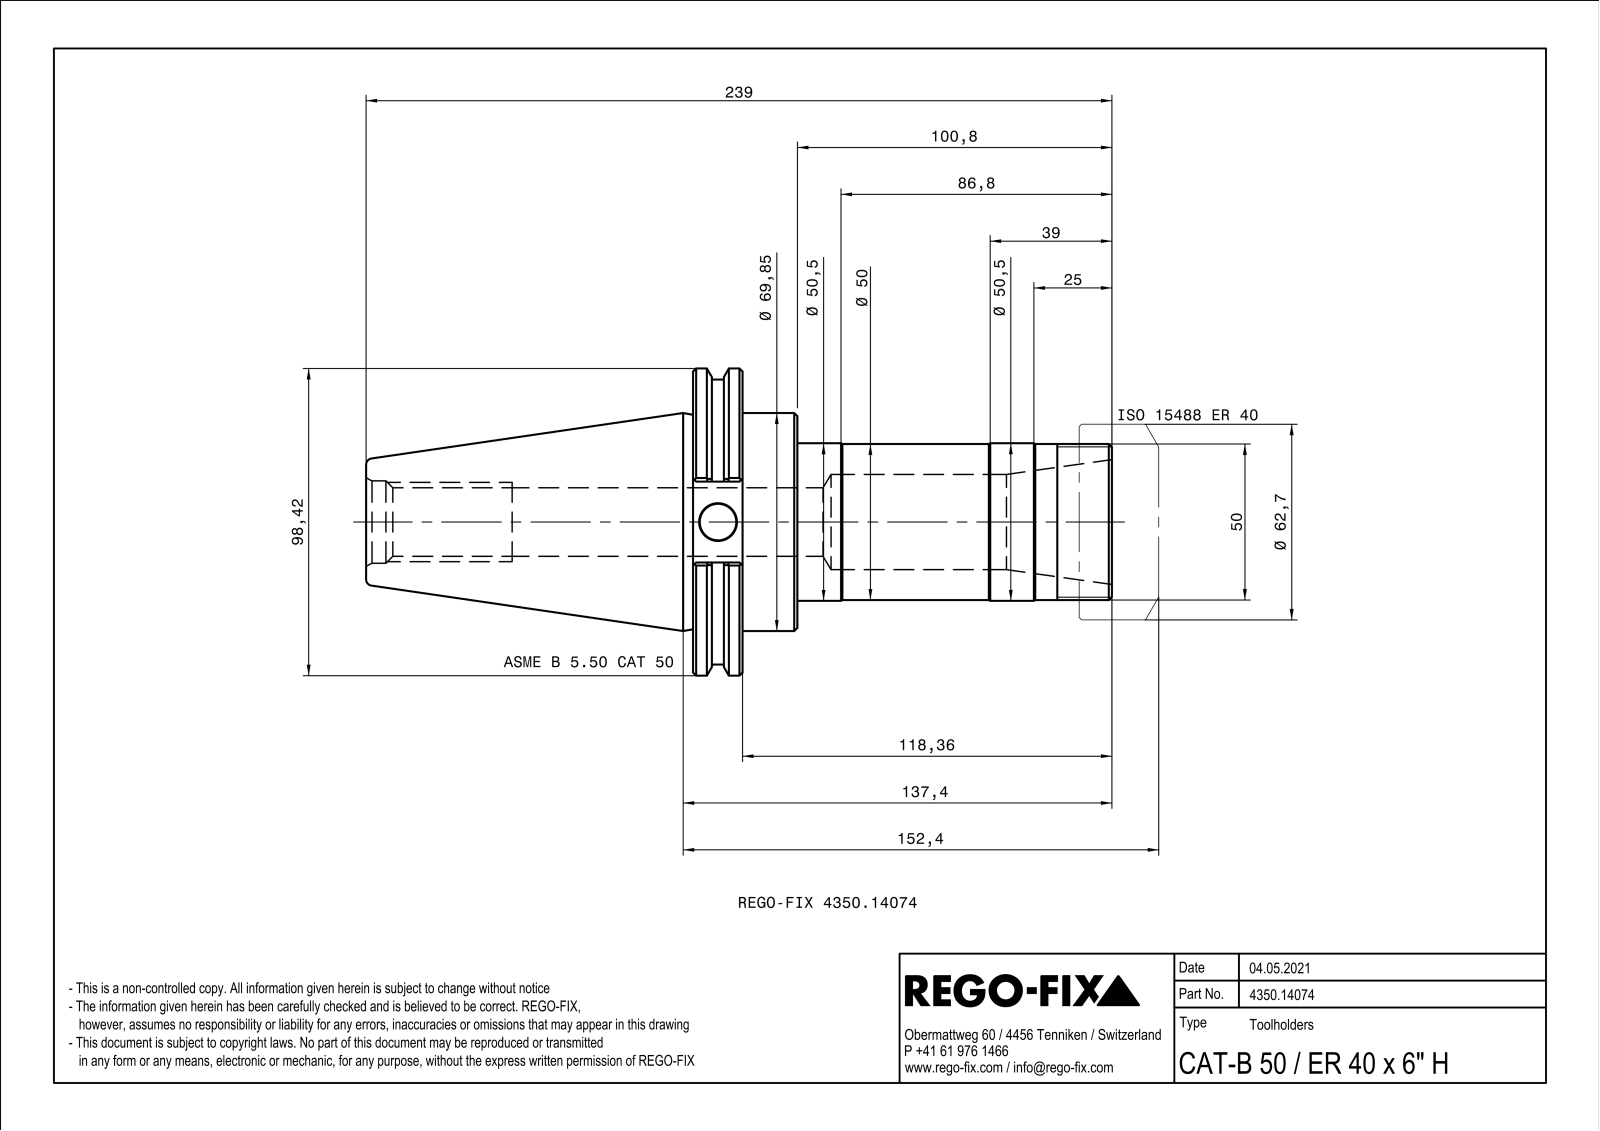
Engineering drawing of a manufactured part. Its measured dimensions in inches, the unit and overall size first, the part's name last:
Units: inches
Overall size (bounding box): 9.409 × 3.875 × 3.716
Round holes (diameter × count): ⌀0.128 ×2, ⌀0.154 ×2, ⌀0.461 ×1, ⌀0.865 ×1, ⌀0.865 ×1, ⌀1.039 ×1, ⌀1.201 ×1
Round bosses / shafts (diameter × count): ⌀3.875 ×1, ⌀3.594 ×1, ⌀2.75 ×1, ⌀1.988 ×1, ⌀1.969 ×1
Partial cylindrical surfaces — rounded edges, fillets, slot ends (radius × count): R0.02 ×12
Main face-to-face distances: 0.625, 0.691, 1.316, 3.969, 4.66, 5.285, 9.409, 5.441, 4.75, 4.125
Volume: 30.29 in³ · Surface area: 116.1 in²
Bodies: 1 solid, 127 faces (35 planar, 44 cylindrical, 48 other)
Part name (STEP PRODUCT): NOCUT
STEP written by: SIEMENS PLM Software Solid Edge ST10 (AUTOMOTIVE_DESIGN)
